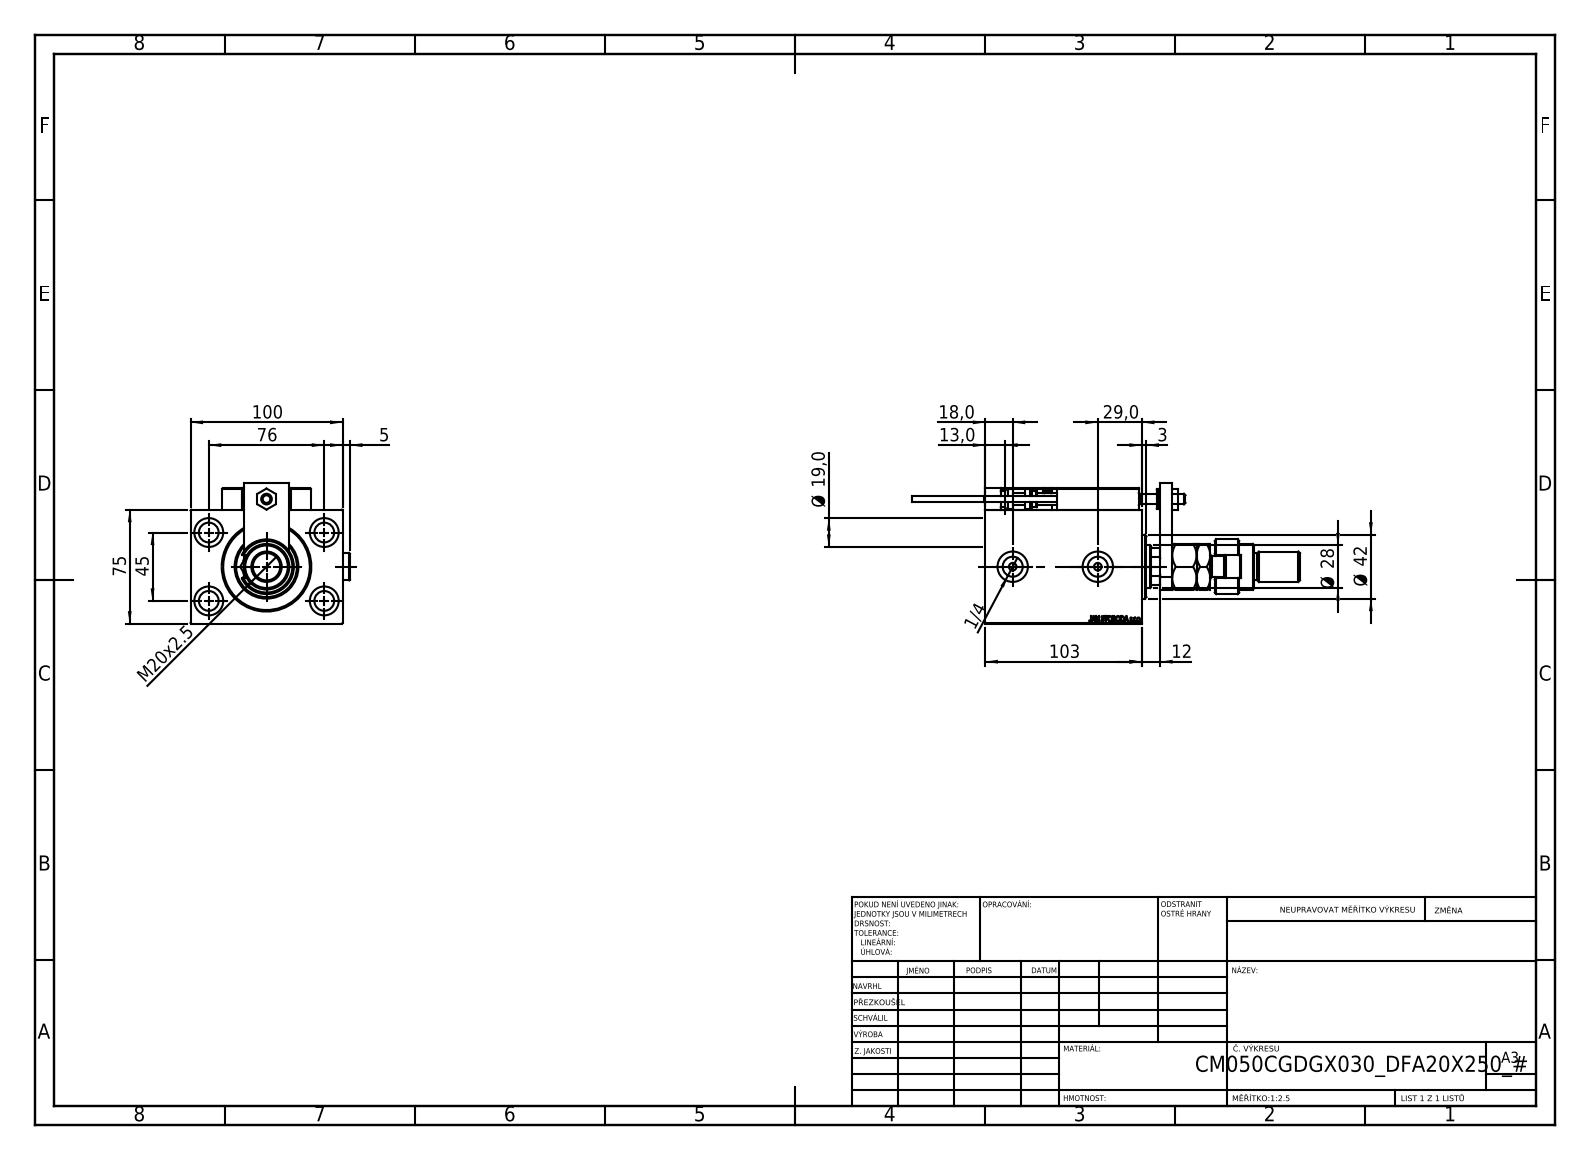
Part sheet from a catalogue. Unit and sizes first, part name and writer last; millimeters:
Units: millimetres
Overall size (bounding box): 255 × 104.9 × 92.5
Round holes (diameter × count): ⌀8 ×5, ⌀3.2 ×4, ⌀4 ×4, ⌀5 ×4, ⌀13 ×4, ⌀19 ×4, ⌀20 ×3, ⌀13.16 ×2, ⌀7 ×1, ⌀18.5 ×1, ⌀28 ×1, ⌀31.5 ×1
Round bosses / shafts (diameter × count): ⌀18 ×3, ⌀5 ×2, ⌀3.8 ×2, ⌀42 ×1, ⌀36 ×1, ⌀30 ×1, ⌀22 ×1, ⌀14 ×1
Partial cylindrical surfaces — rounded edges, fillets, slot ends (radius × count): R0.3 ×30, R3 ×2, R7.5 ×1, R12 ×1, R13.5 ×1
Main face-to-face distances: 75, 14, 100, 89, 103, 12, 20, 30, 8, 45
Hole centre spacings: 44.16, 11.37, 20, 29.59, 29.69, 36.06, 42.19, 43.91
Volume: 761 960 mm³ · Surface area: 152 384 mm²
Bodies: 27 solids, 1424 faces (623 planar, 219 cylindrical, 582 other)
Part name (STEP PRODUCT): X_Y_DFA; V450CM_C_Body; KONCOVKA; TYC_L79 (+7 more)
STEP written by: SolidWorks 2019 (CONFIG_CONTROL_DESIGN)
